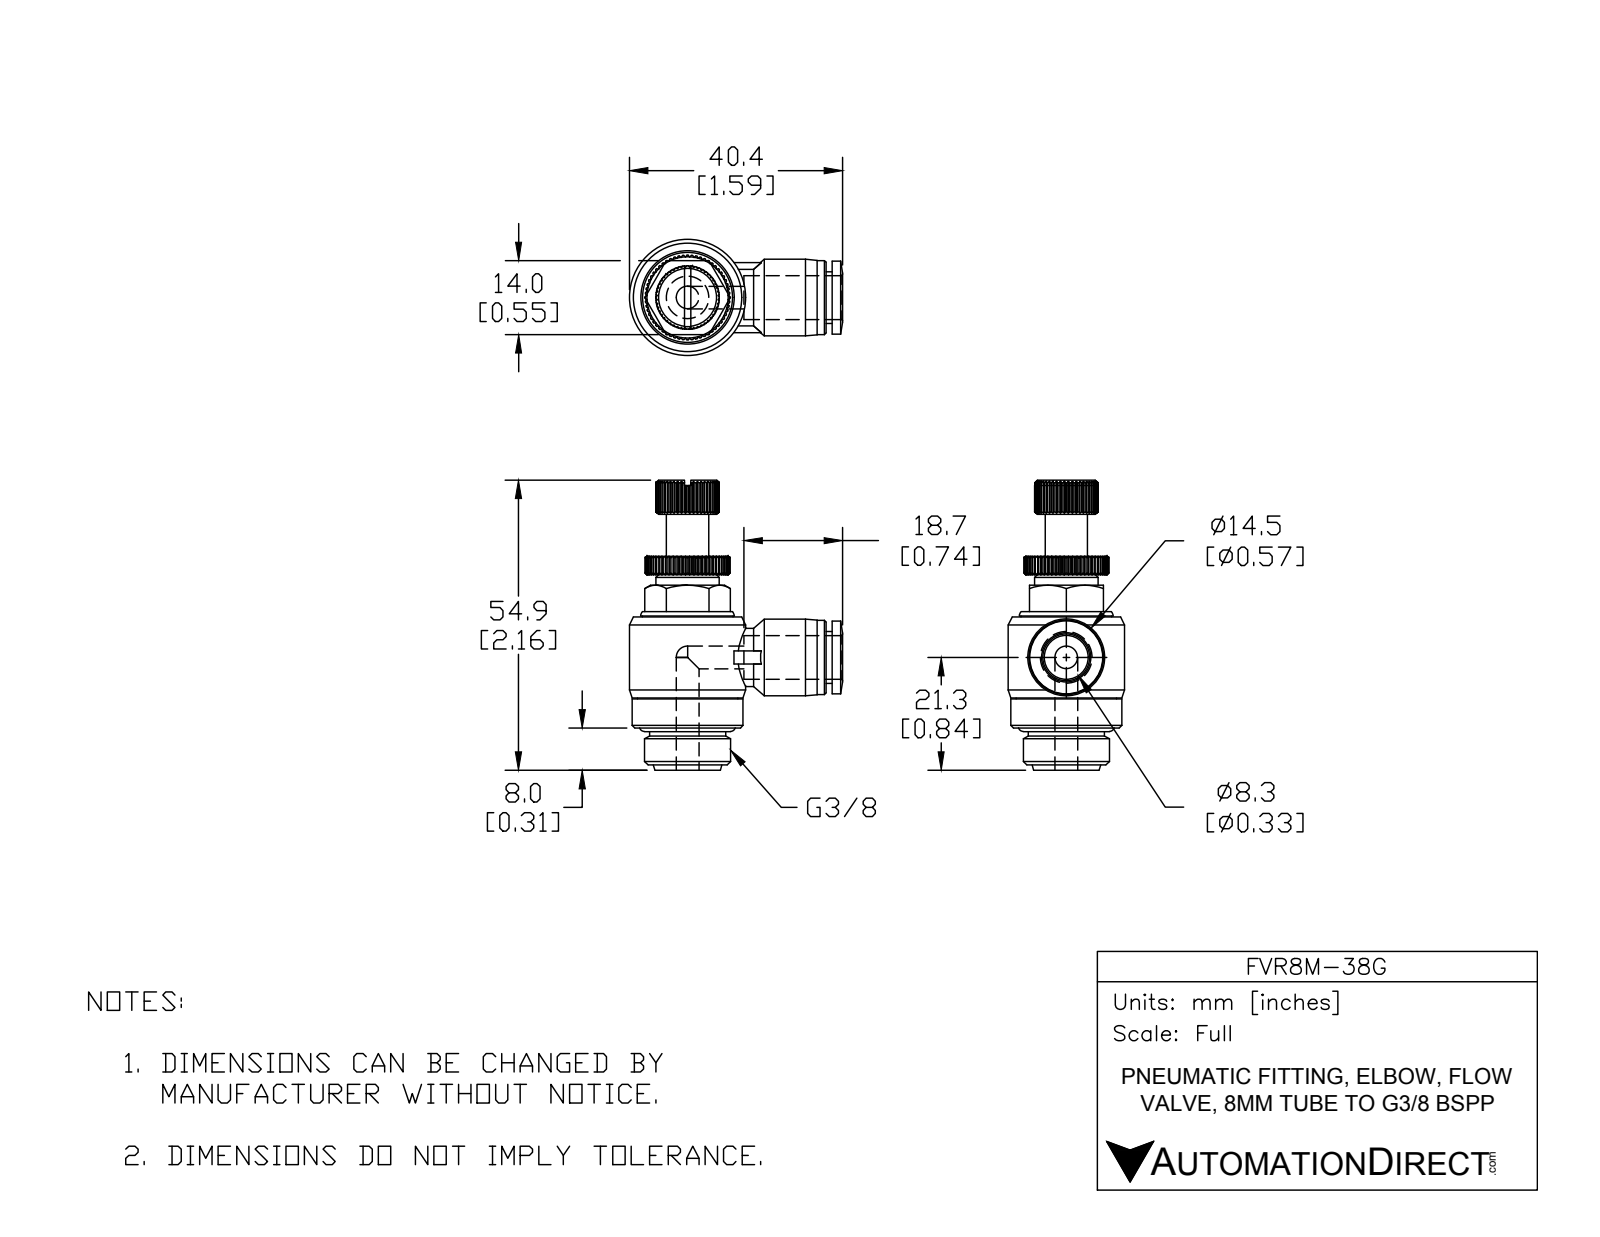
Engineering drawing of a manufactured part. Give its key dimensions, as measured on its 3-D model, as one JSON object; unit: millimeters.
{"part_name": "FVR8M-38G", "step_written_by": "SolidWorks 2015 (AUTOMOTIVE_DESIGN)", "units": "millimeters", "bodies": {"solids": 2, "faces": 567, "planar": 251, "cylindrical": 143, "other": 173}, "overall_size": [54.9, 40.4, 22], "volume_mm3": 13600, "surface_area_mm2": 6345, "round_holes": [[4.3, 2], [8.3, 1]], "round_bosses_or_shafts": [[22, 1], [21, 1], [19, 1], [17.1, 1], [16.3, 1], [14.5, 1], [14.4, 1], [14, 1]], "partial_cylinders_radius": [[8, 1]], "face_to_face_distances": [29, 8, 14, 1, 40.5, 27, 11.5, 7, 14.4, 17.9]}
